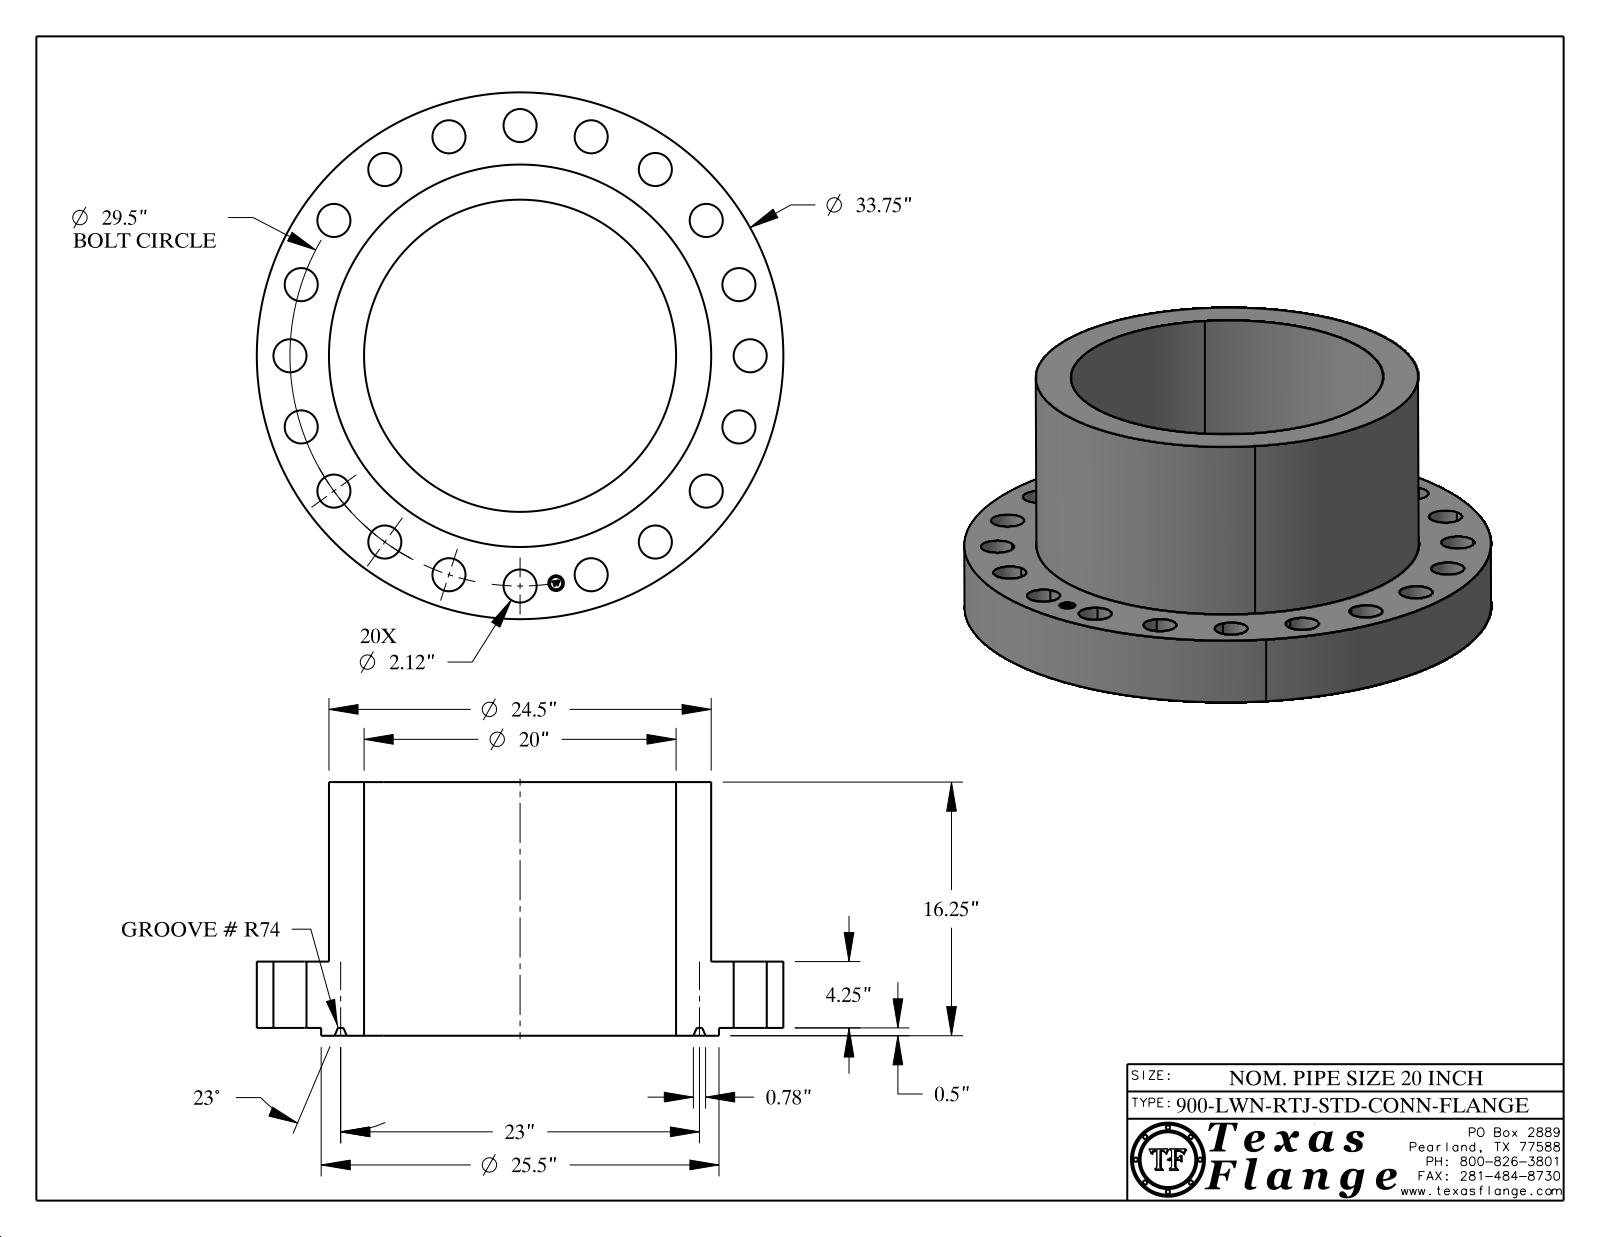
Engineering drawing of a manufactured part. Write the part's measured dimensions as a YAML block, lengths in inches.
part_name: "20-900-LWN-RTJ-STD-CONN-FLANGE"
step_written_by: "CATIA V5 STEP AP214 (AUTOMOTIVE_DESIGN)"
units: inches
bodies: {solids: 1, faces: 447, planar: 371, cylindrical: 68, other: 8}
overall_size: [33.75, 33.75, 16.25]
volume: 4053
surface_area: 4029
round_holes:
  - {diameter: 2.12, count: 20}
  - {diameter: 1, count: 1}
  - {diameter: 20, count: 1}
round_bosses_or_shafts:
  - {diameter: 0.061, count: 8}
  - {diameter: 33.75, count: 1}
  - {diameter: 25.5, count: 1}
  - {diameter: 24.5, count: 1}
  - {diameter: 0.788, count: 1}
face_to_face_distances: [4.25, 15.75, 11.5, 0.5, 4.75, 16.25, 4.745, 4.245, 11.505, 0.298]
hole_center_spacings: [14.75, 29.137, 4.615, 17.34, 20.859, 23.866, 26.285, 9.116]
